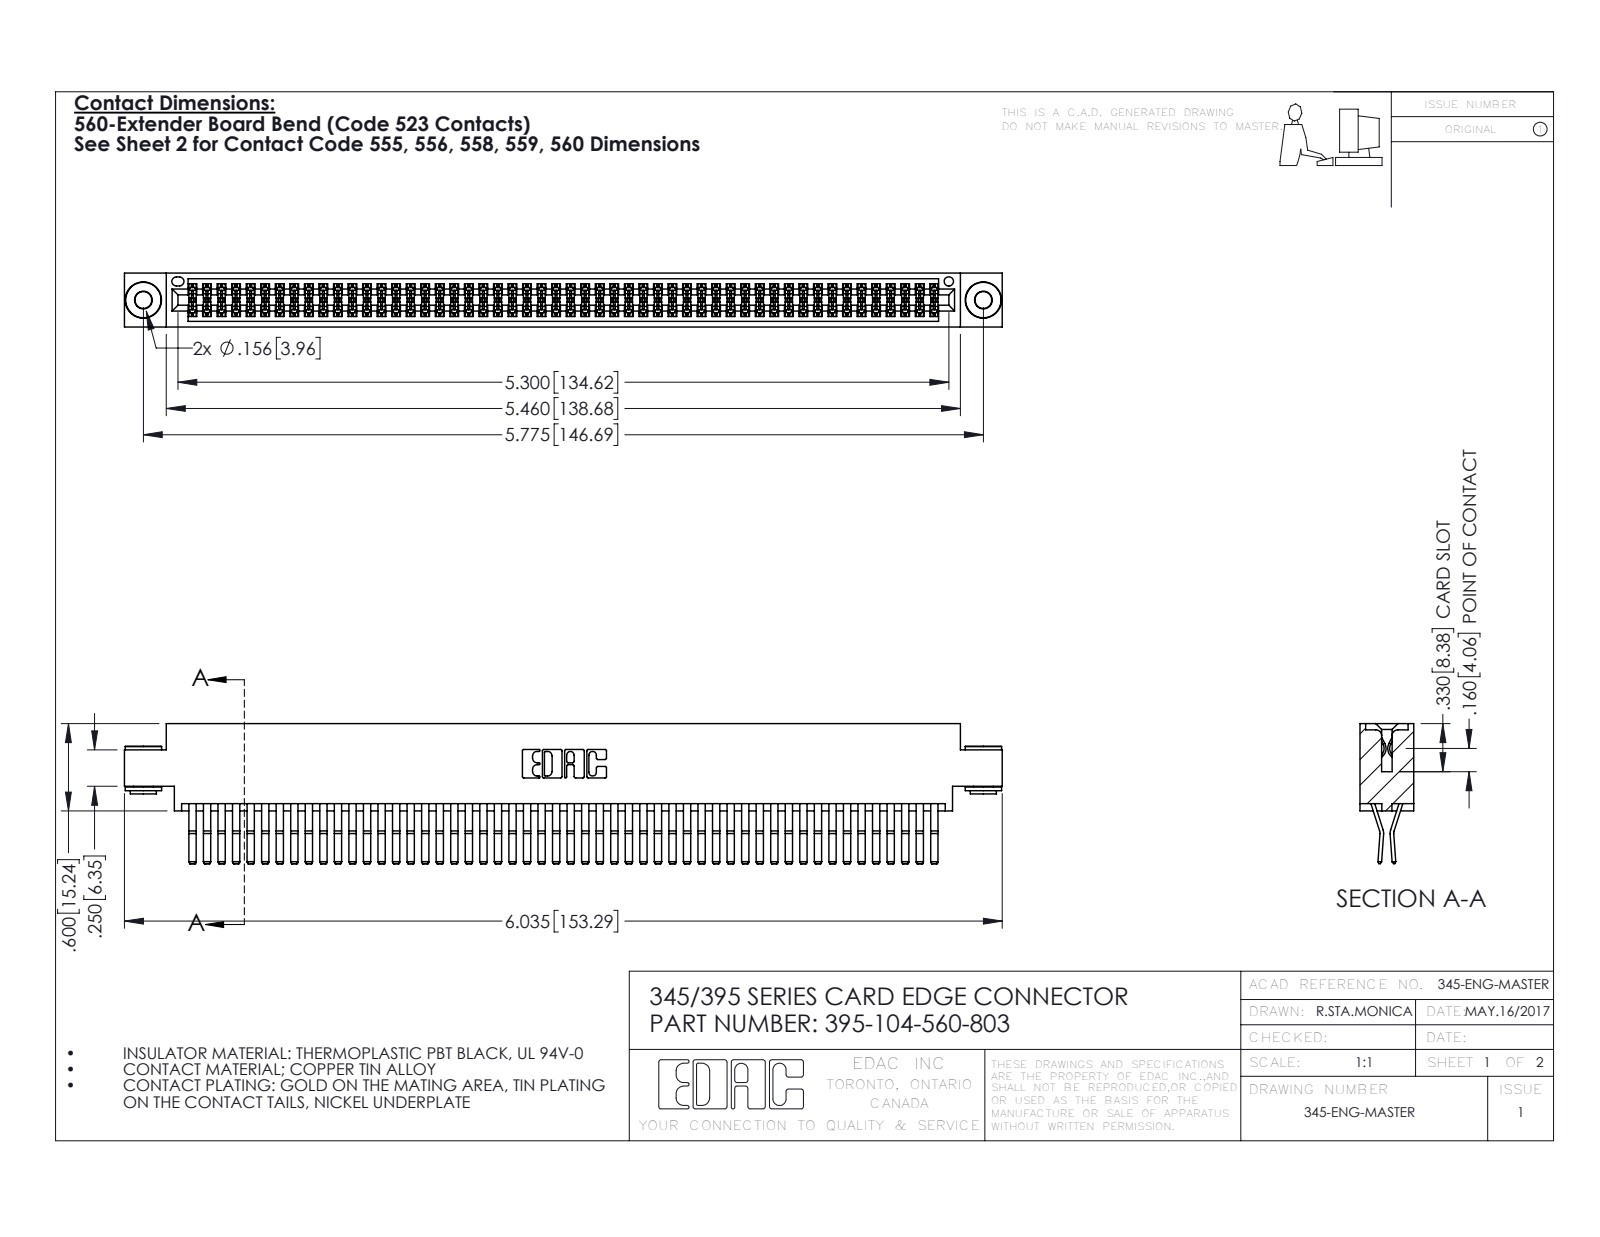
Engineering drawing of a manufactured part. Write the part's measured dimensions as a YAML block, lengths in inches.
part_name: "345 Part_0.170 Offset - 0.156 Dia-TH; 345-250-002_345-250-002-102; 345-292-001_560 Tail; 395-104-560-803"
step_written_by: "SolidWorks 2016 (CONFIG_CONTROL_DESIGN)"
units: inches
bodies: {solids: 107, faces: 5576, planar: 3526, cylindrical: 2042, other: 8}
overall_size: [6.035, 0.962, 0.37]
volume: 0.95
surface_area: 39.23
round_holes:
  - {diameter: 0.116, count: 2}
  - {diameter: 0.156, count: 2}
  - {diameter: 0.064, count: 1}
round_bosses_or_shafts:
  - {diameter: 0.25, count: 2}
  - {diameter: 0.18, count: 2}
  - {diameter: 0.136, count: 2}
partial_cylinders:
  - {radius: 0.006, count: 157}
  - {radius: 0.01, count: 22}
  - {radius: 0.007, count: 6}
  - {radius: 0.031, count: 6}
  - {radius: 0.026, count: 3}
  - {radius: 0.01, count: 2}
  - {radius: 0.014, count: 2}
  - {radius: 0.019, count: 2}
face_to_face_distances: [0.025, 0.072, 0.298, 0.37, 0.2, 0.098, 0.272, 0.225, 0.175, 0.149]
hole_center_spacings: [0.27, 5.539, 5.775]
